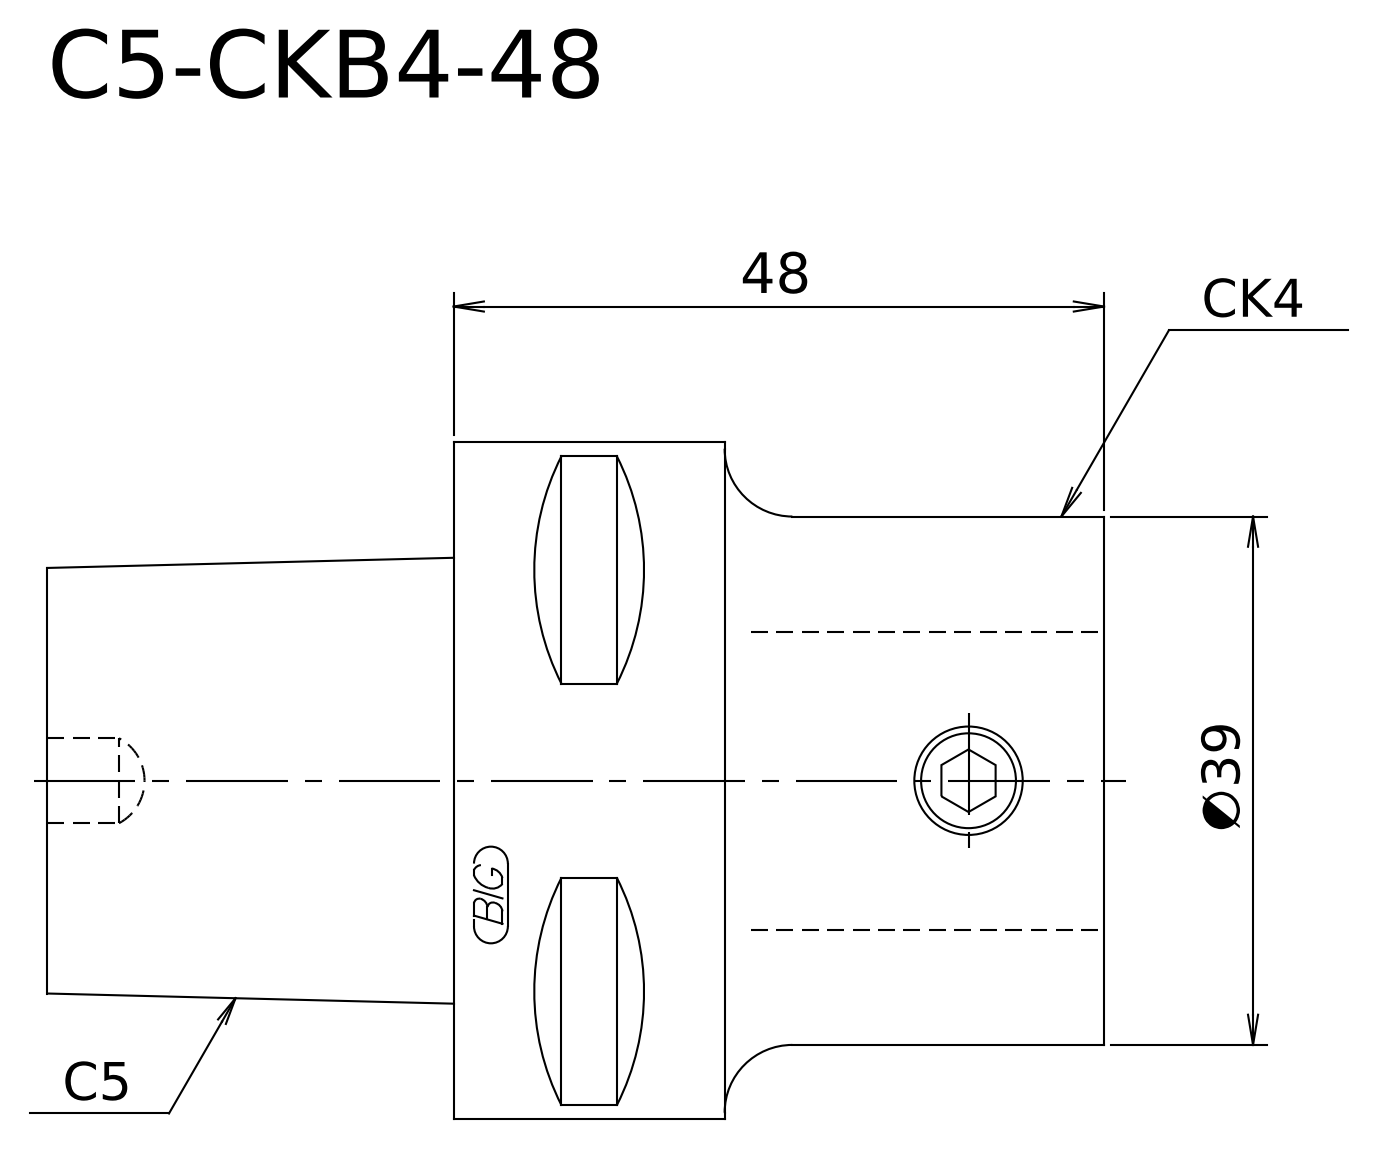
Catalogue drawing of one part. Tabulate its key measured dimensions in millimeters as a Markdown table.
| quantity | value |
| --- | --- |
| STEP written by | Kubotek KeyCreator V8.5.1 (14335) (CONFIG_CONTROL_DESIGN) |
| units | millimeters |
| bodies | 1 solid, 8 faces (4 planar, 2 cylindrical, 2 other) |
| overall size | 78 × 49.98 × 49.98 |
| volume | 101 376 mm³ |
| surface area | 13 347 mm² |
| round bosses / shafts (diameter × count) | 49.98 × 1, 39 × 1 |
| main face-to-face distances | 48, 78, 30, 28, 20, 50 |
